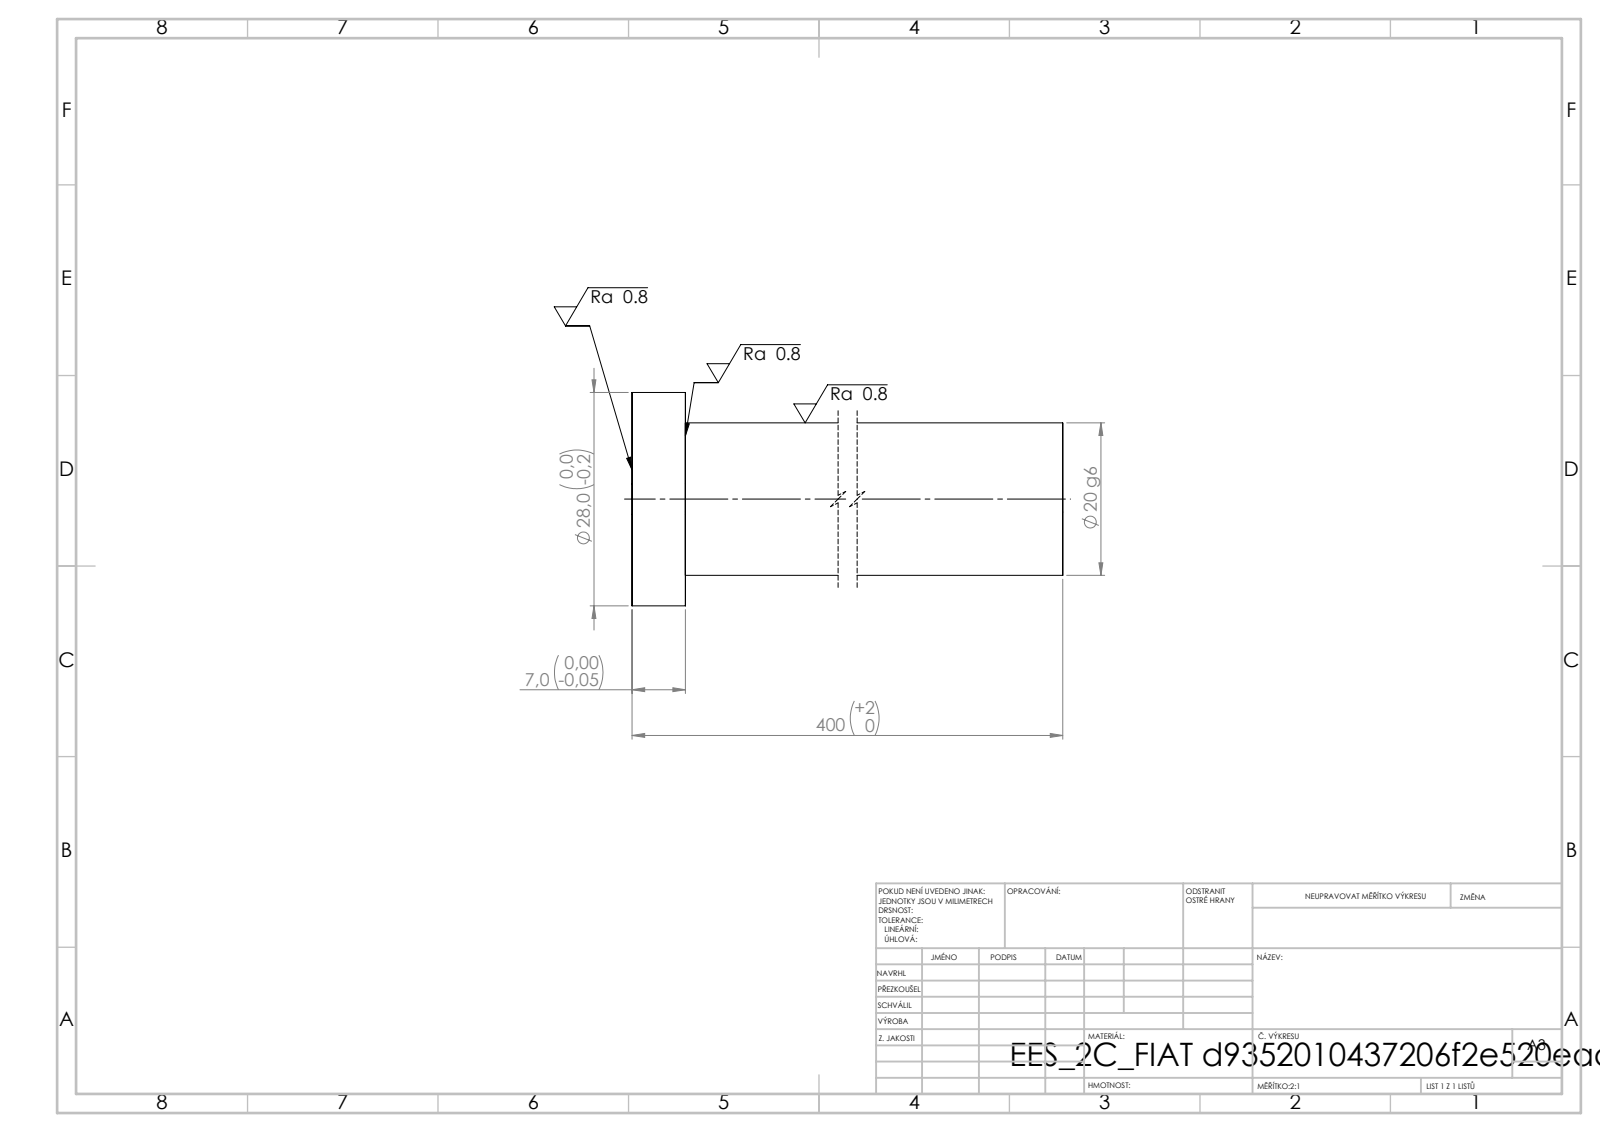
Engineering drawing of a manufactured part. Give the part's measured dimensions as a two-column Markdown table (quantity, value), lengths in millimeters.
| quantity | value |
| --- | --- |
| STEP written by | SolidWorks 2019 (CONFIG_CONTROL_DESIGN) |
| units | millimeters |
| bodies | 1 solid, 7 faces (3 planar, 4 cylindrical, 0 other) |
| overall size | 400 × 28 × 28 |
| volume | 127 775 mm³ |
| surface area | 26 540 mm² |
| round bosses / shafts (diameter × count) | 28 × 1, 20 × 1 |
| main face-to-face distances | 400, 7, 393 |
